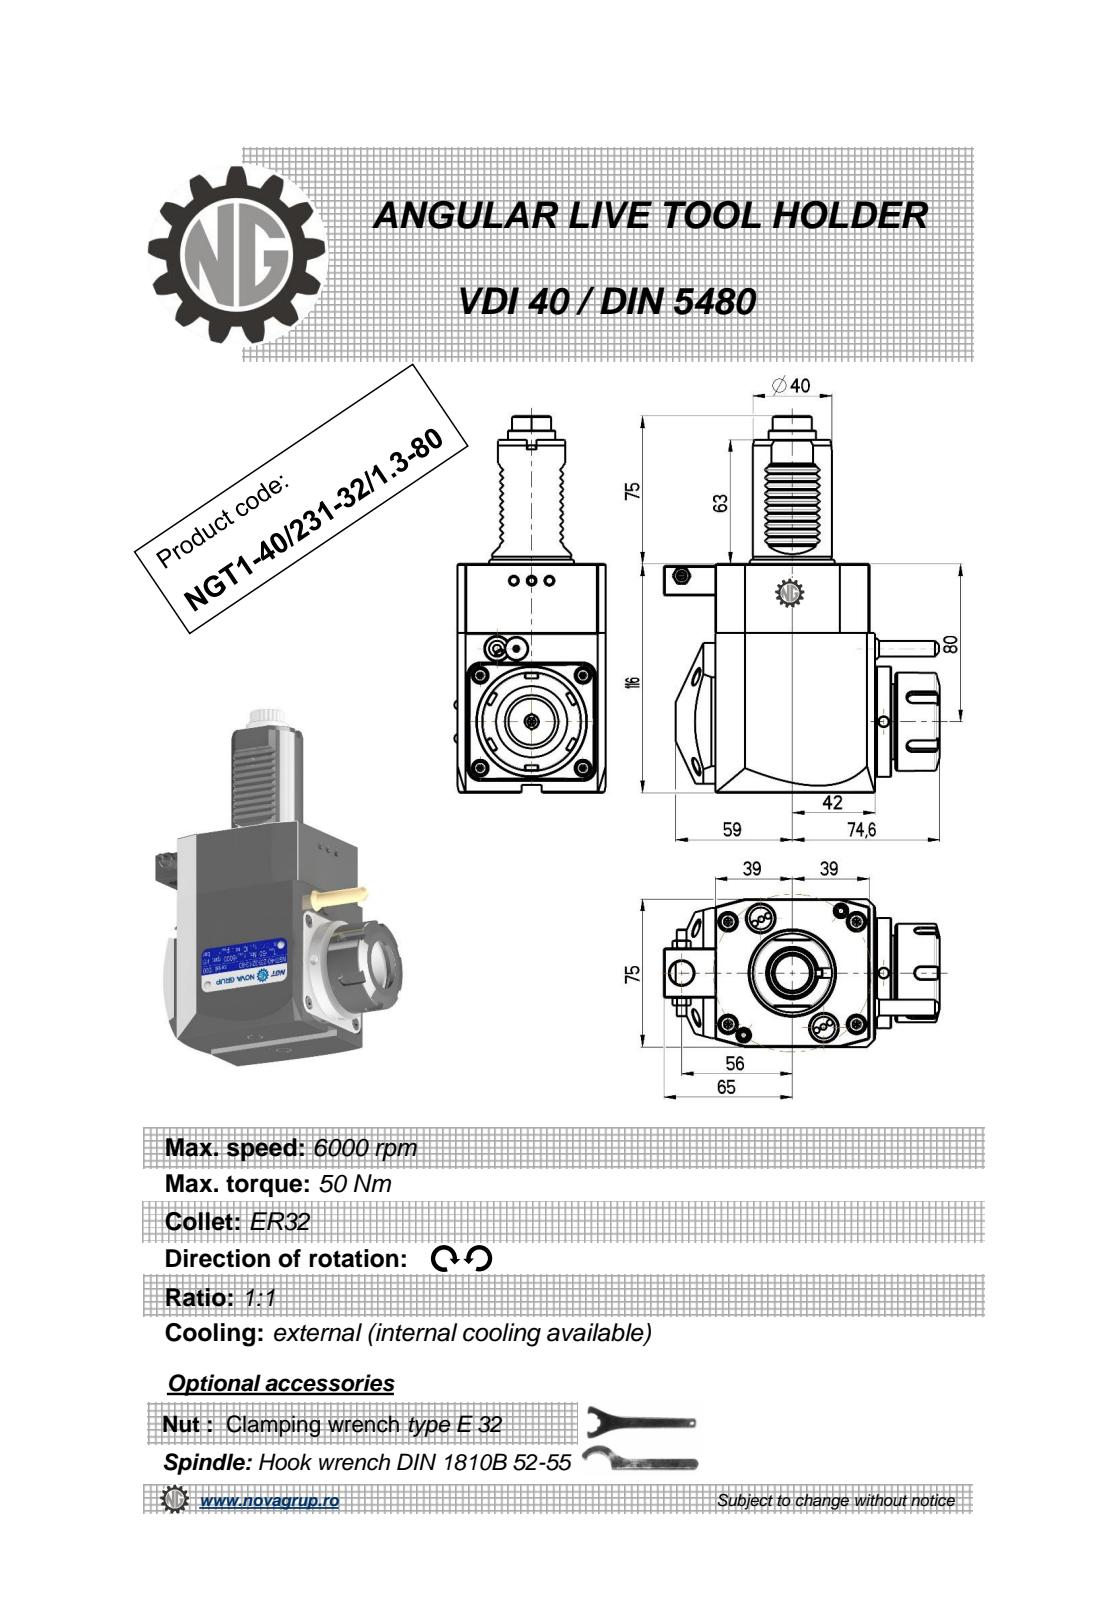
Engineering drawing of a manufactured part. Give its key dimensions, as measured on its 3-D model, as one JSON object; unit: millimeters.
{"part_name": "NGT1_40_231_32_1_3_80", "step_written_by": "PRO/ENGINEER BY PARAMETRIC TECHNOLOGY CORPORATION, 2010280 (CONFIG_CONTROL_DESIGN)", "units": "millimeters", "bodies": {"solids": 1, "faces": 583, "planar": 229, "cylindrical": 191, "other": 163}, "overall_size": [191, 139.6, 75], "volume_mm3": 881467, "surface_area_mm2": 71709, "round_holes": [[5, 3], [3, 1], [4.2, 1], [9.5, 1], [12, 1], [27, 1]], "round_bosses_or_shafts": [[56, 1], [50, 1], [43, 1], [40, 1], [24, 1], [11.2, 1], [8.96, 1], [8, 1]], "partial_cylinders_radius": [[2.08, 48], [0.3, 20], [0.26, 12], [0.22, 6], [3, 5], [9.08, 1], [9.92, 1], [15, 1]], "face_to_face_distances": [75, 116, 81, 78, 3, 7.5, 80.8, 2.8, 0.5, 4.5], "hole_center_spacings": [38.68, 40.93, 71.5, 102.25, 126.22]}
